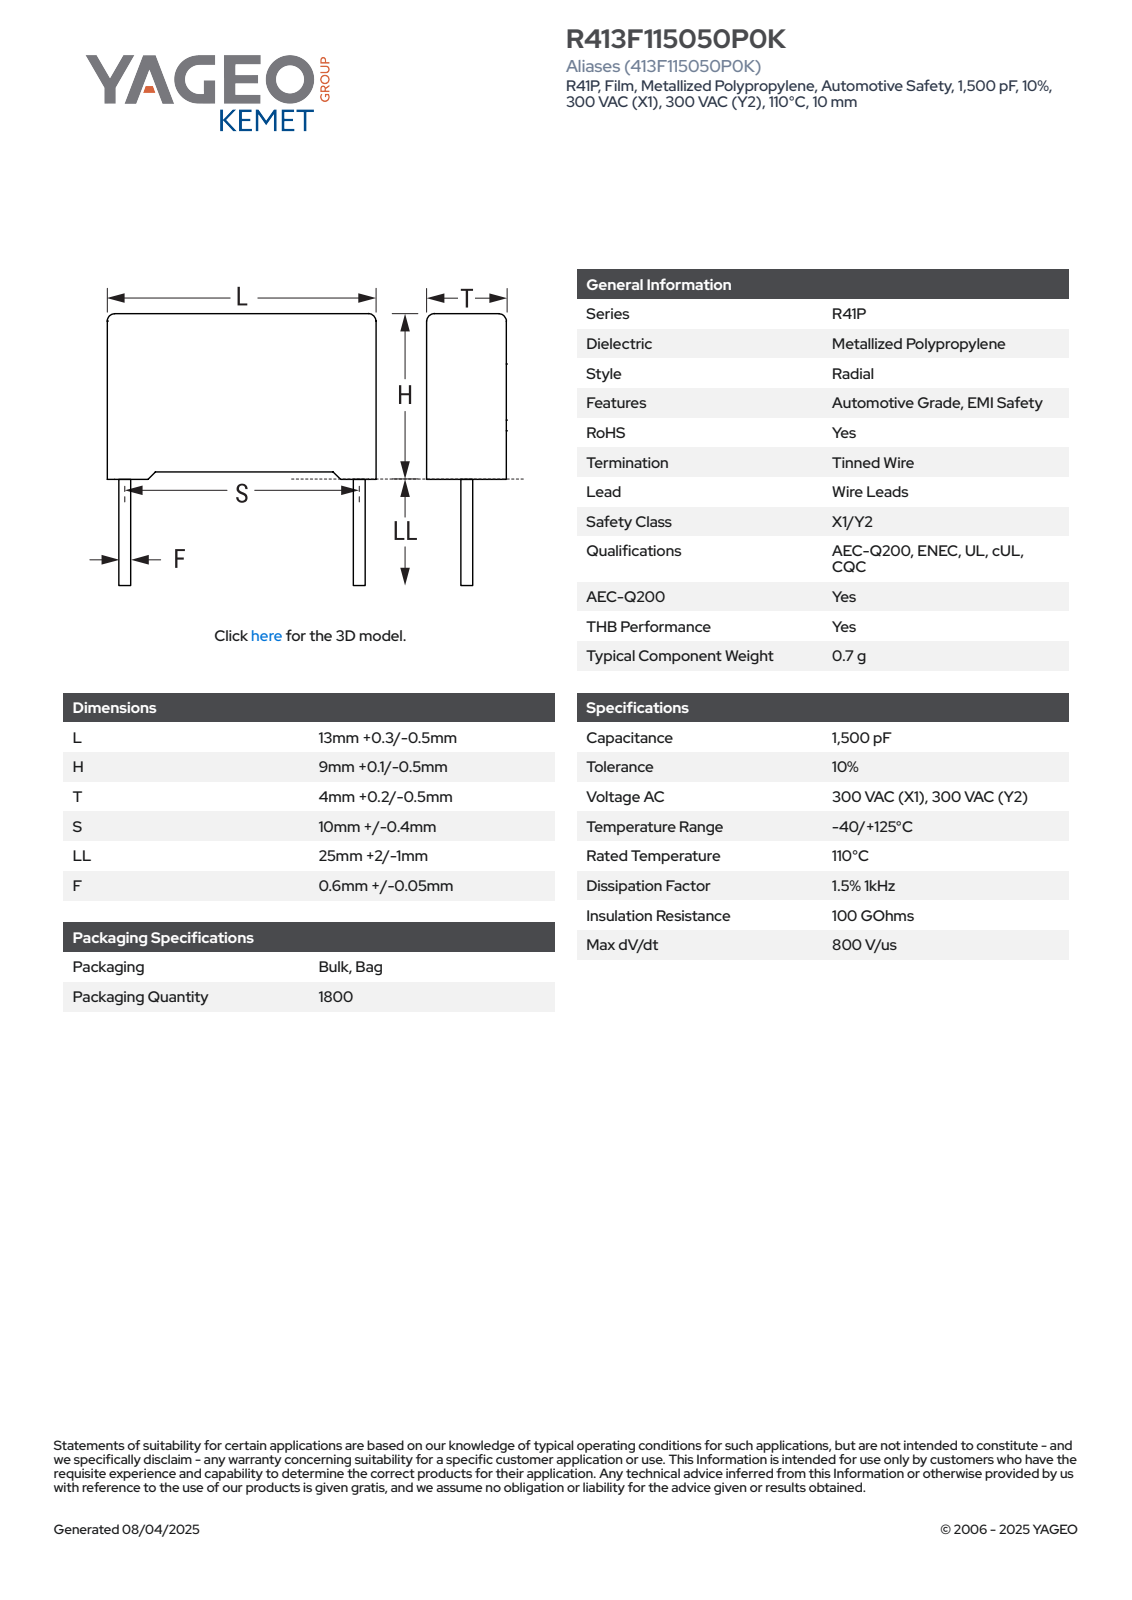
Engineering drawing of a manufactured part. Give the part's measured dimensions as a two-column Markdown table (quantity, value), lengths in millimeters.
| quantity | value |
| --- | --- |
| part name | CFR_RB2_13X9X4_L13.3H9.1T4.2S10LL27F0.65 |
| STEP written by | SolidWorks 2021 (AUTOMOTIVE_DESIGN) |
| units | millimeters |
| bodies | 4 solids, 85 faces (77 planar, 8 cylindrical, 0 other) |
| overall size | 36.1 × 13.3 × 4.21 |
| volume | 492 mm³ |
| surface area | 565 mm² |
| round bosses / shafts (diameter × count) | 0.65 × 2 |
| partial cylindrical surfaces (radius × count) | 0.5 × 4 |
| main face-to-face distances | 4.2, 8.35, 13.3, 0.44, 3.76, 0.75, 9.1, 3.32, 0.31, 8.79 |
